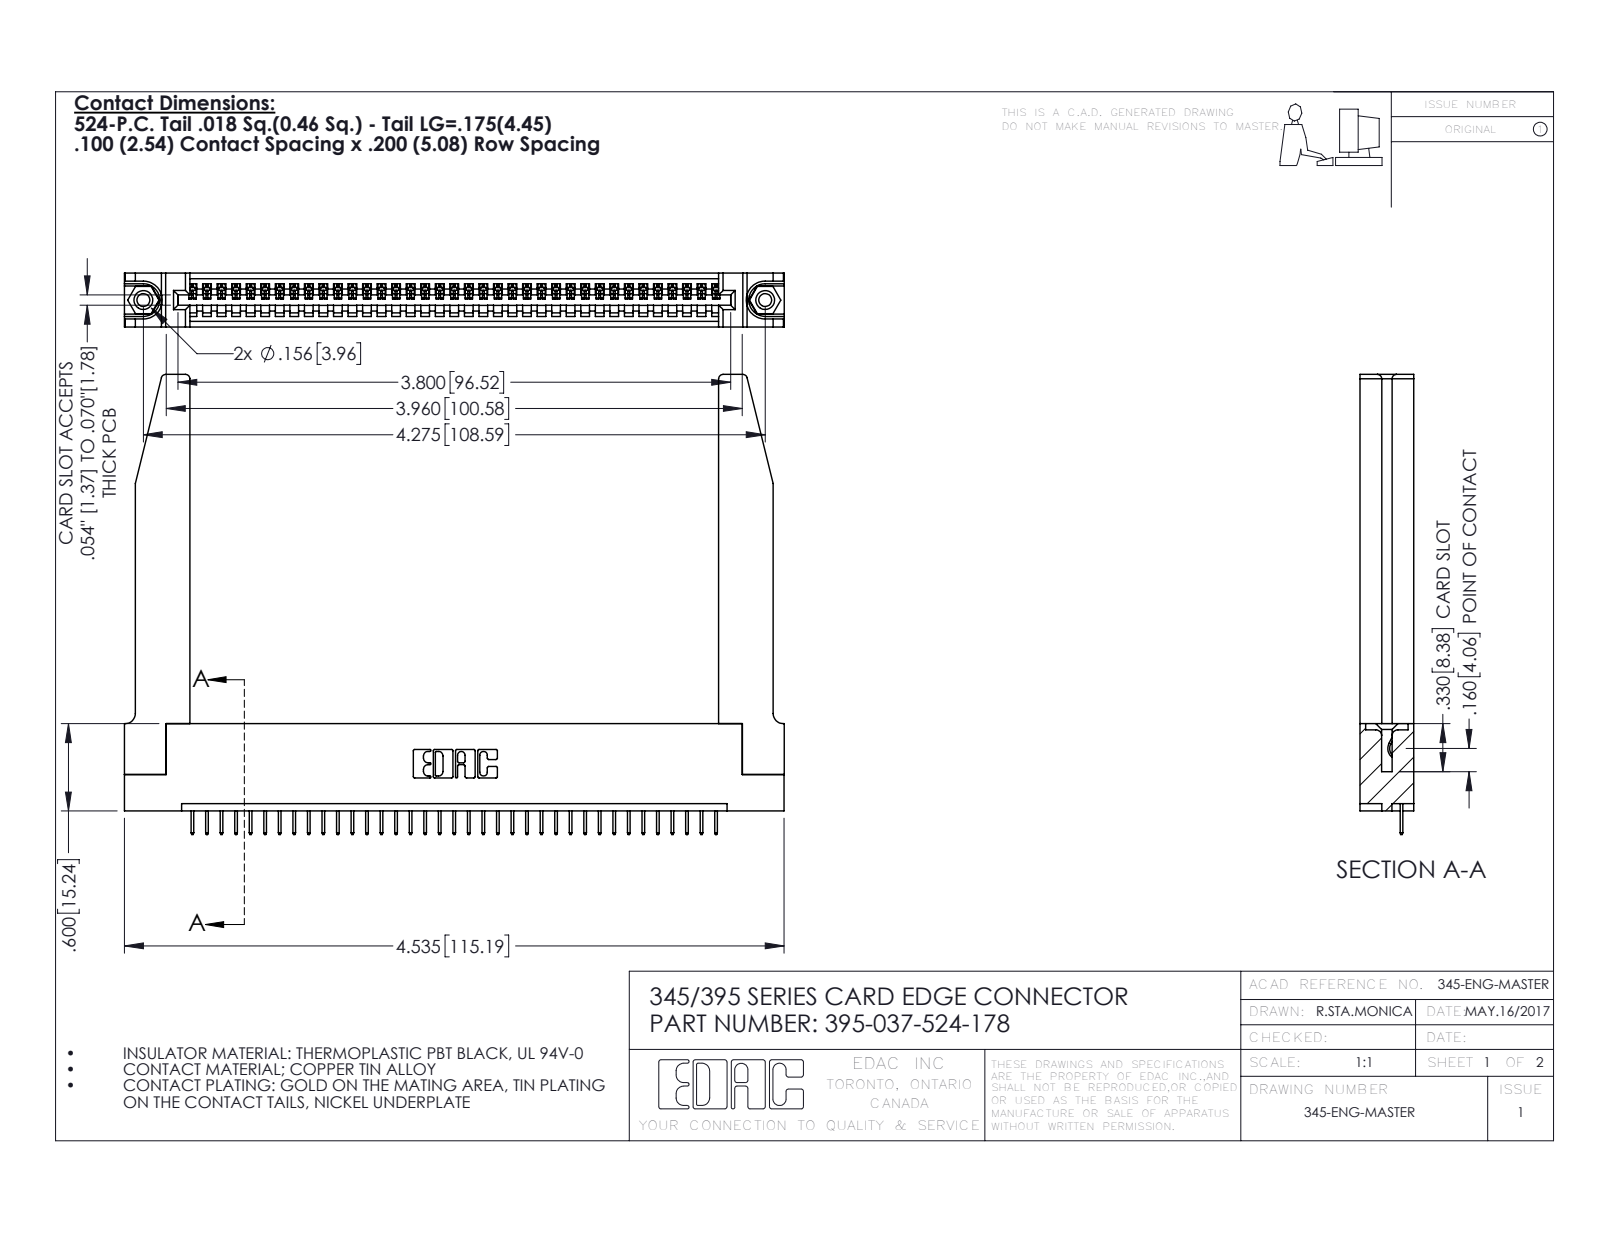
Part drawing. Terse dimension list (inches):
name: 345-250-001_345-250-001-102; 345-220-078_345-220-078; 395-037-524-178; 345-292-001_345-293-124 (+1 more)
written by: SolidWorks 2016 (CONFIG_CONTROL_DESIGN)
unit: in
bodies: 42 solids, 2654 faces (1924 planar, 678 cylindrical, 52 other)
size: 4.536 × 3.162 × 0.37
volume: 1.131 in³; area: 31.94 in²
holes: 2× ⌀0.089, 2× ⌀0.125, 2× ⌀0.156, 1× ⌀0.064
bosses: 2× ⌀0.155
rounds: 74× R0.006, 22× R0.01, 8× R0.03, 6× R0.007, 6× R0.031, 3× R0.026, 2× R0.031, 2× R0.04
face distances: 0.37, 0.072, 0.298, 0.2, 0.098, 0.272, 0.025, 0.225, 0.15, 0.148
hole spacings: 0.27, 4.039, 4.275
